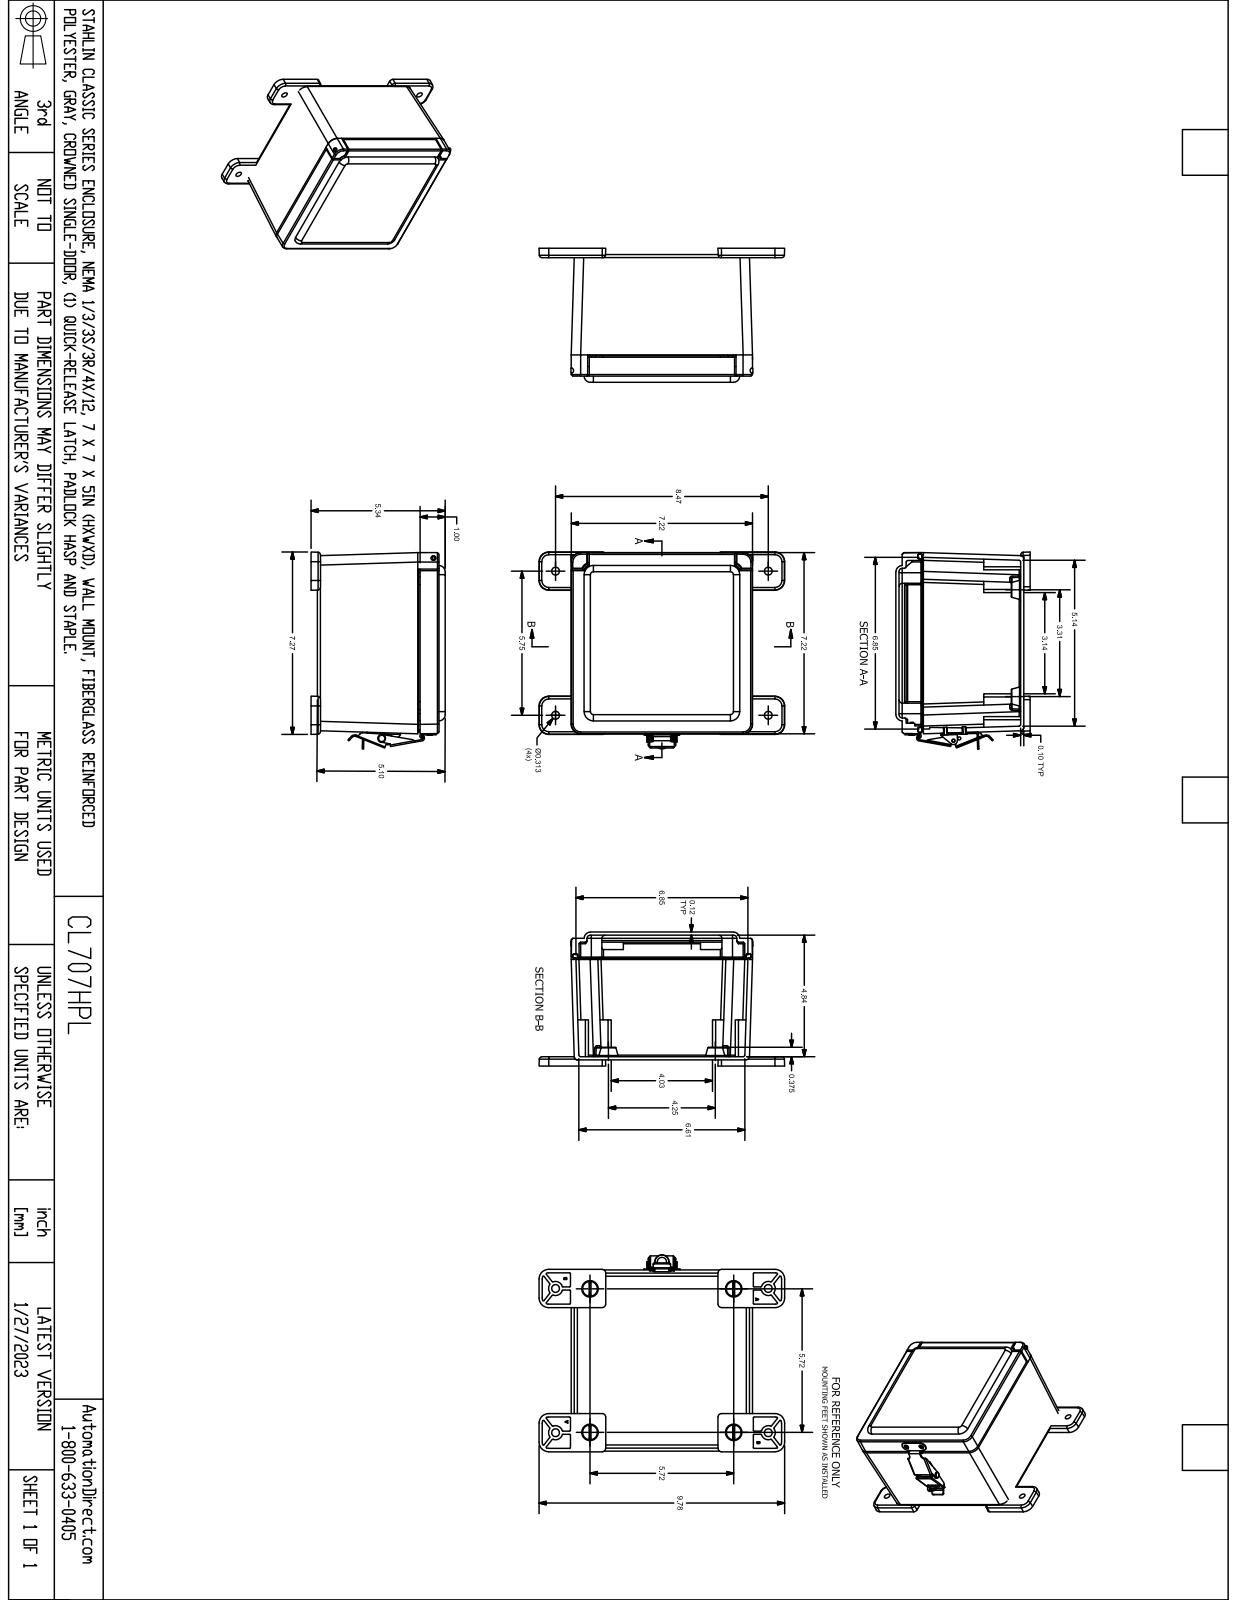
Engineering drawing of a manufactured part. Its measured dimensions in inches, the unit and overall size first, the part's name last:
Units: inches
Overall size (bounding box): 9.783 × 7.85 × 5.344
Round holes (diameter × count): ⌀0.159 ×6, ⌀0.281 ×6, ⌀0.14 ×4, ⌀0.313 ×4, ⌀0.313 ×4, ⌀0.344 ×4, ⌀0.531 ×4, ⌀0.075 ×2, ⌀0.096 ×2, ⌀0.104 ×2, ⌀0.13 ×2, ⌀0.13 ×2
Round bosses / shafts (diameter × count): ⌀0.27 ×6, ⌀0.229 ×4, ⌀0.125 ×3, ⌀0.375 ×2, ⌀0.125 ×2, ⌀0.325 ×1, ⌀0.325 ×1, ⌀0.3 ×1
Partial cylindrical surfaces — rounded edges, fillets, slot ends (radius × count): R0.031 ×56, R0.031 ×50, R0.125 ×34, R0.062 ×17, R0.063 ×12, R0.1 ×12, R0.25 ×12, R0.375 ×10
Main face-to-face distances: 0.125, 4.969, 5.094, 0.186, 0.186, 4.844, 0.25, 0.125, 5.219, 0.75
Hole centre spacings: 8.09, 0.75, 1.039, 1.375, 2.239, 5.039, 5.04, 5.426
Volume: 54.59 in³ · Surface area: 617.9 in²
Bodies: 36 solids, 1543 faces (664 planar, 454 cylindrical, 425 other)
Part name (STEP PRODUCT): CE707HPL
STEP written by: SolidWorks 2018 (AUTOMOTIVE_DESIGN)
